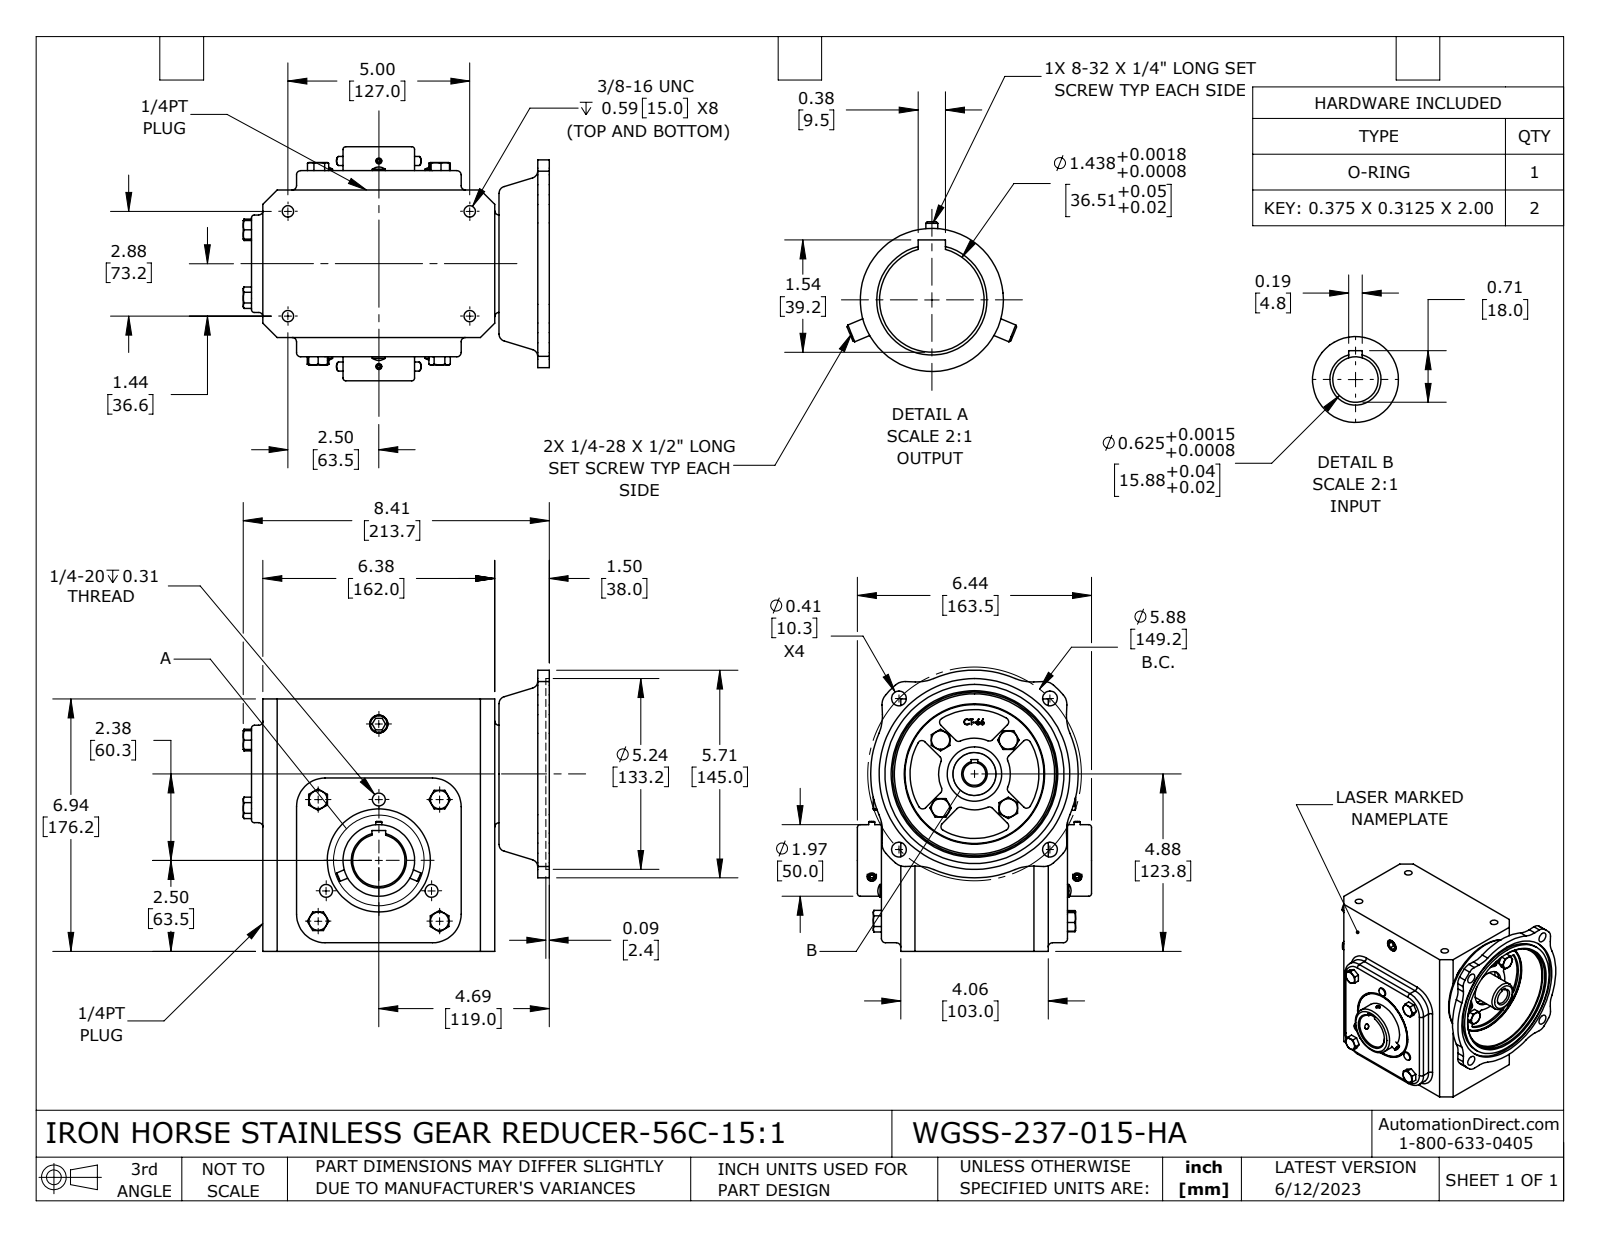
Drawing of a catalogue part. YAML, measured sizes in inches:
part_name: "WGSS-237-015-HA"
step_written_by: "SolidWorks 2021 (CONFIG_CONTROL_DESIGN)"
units: inches
bodies: {solids: 7, faces: 670, planar: 287, cylindrical: 195, other: 188}
overall_size: [8.412, 7.729, 6.437]
volume: 204.5
surface_area: 348.1
round_holes:
  - {diameter: 0.213, count: 4}
  - {diameter: 0.313, count: 4}
  - {diameter: 0.406, count: 4}
  - {diameter: 0.136, count: 2}
  - {diameter: 0.625, count: 1}
  - {diameter: 0.866, count: 1}
  - {diameter: 1.437, count: 1}
  - {diameter: 1.441, count: 1}
  - {diameter: 1.496, count: 1}
  - {diameter: 1.772, count: 1}
  - {diameter: 3.819, count: 1}
  - {diameter: 4.5, count: 1}
round_bosses_or_shafts:
  - {diameter: 0.25, count: 4}
  - {diameter: 0.354, count: 3}
  - {diameter: 0.164, count: 2}
  - {diameter: 4.921, count: 1}
  - {diameter: 2.835, count: 1}
  - {diameter: 1.969, count: 1}
  - {diameter: 1.181, count: 1}
partial_cylinders:
  - {radius: 0.118, count: 40}
  - {radius: 0.394, count: 12}
  - {radius: 1.181, count: 8}
  - {radius: 0.079, count: 4}
  - {radius: 0.787, count: 4}
  - {radius: 0.984, count: 1}
  - {radius: 1.772, count: 1}
  - {radius: 2.854, count: 1}
face_to_face_distances: [0.531, 4.587, 6.937, 0.315, 4.055, 6.378, 5.118, 7.874, 1.181, 6.693]
hole_center_spacings: [2.858, 2.937, 4.944, 5.65, 2.88, 4.154, 4.154, 5]
